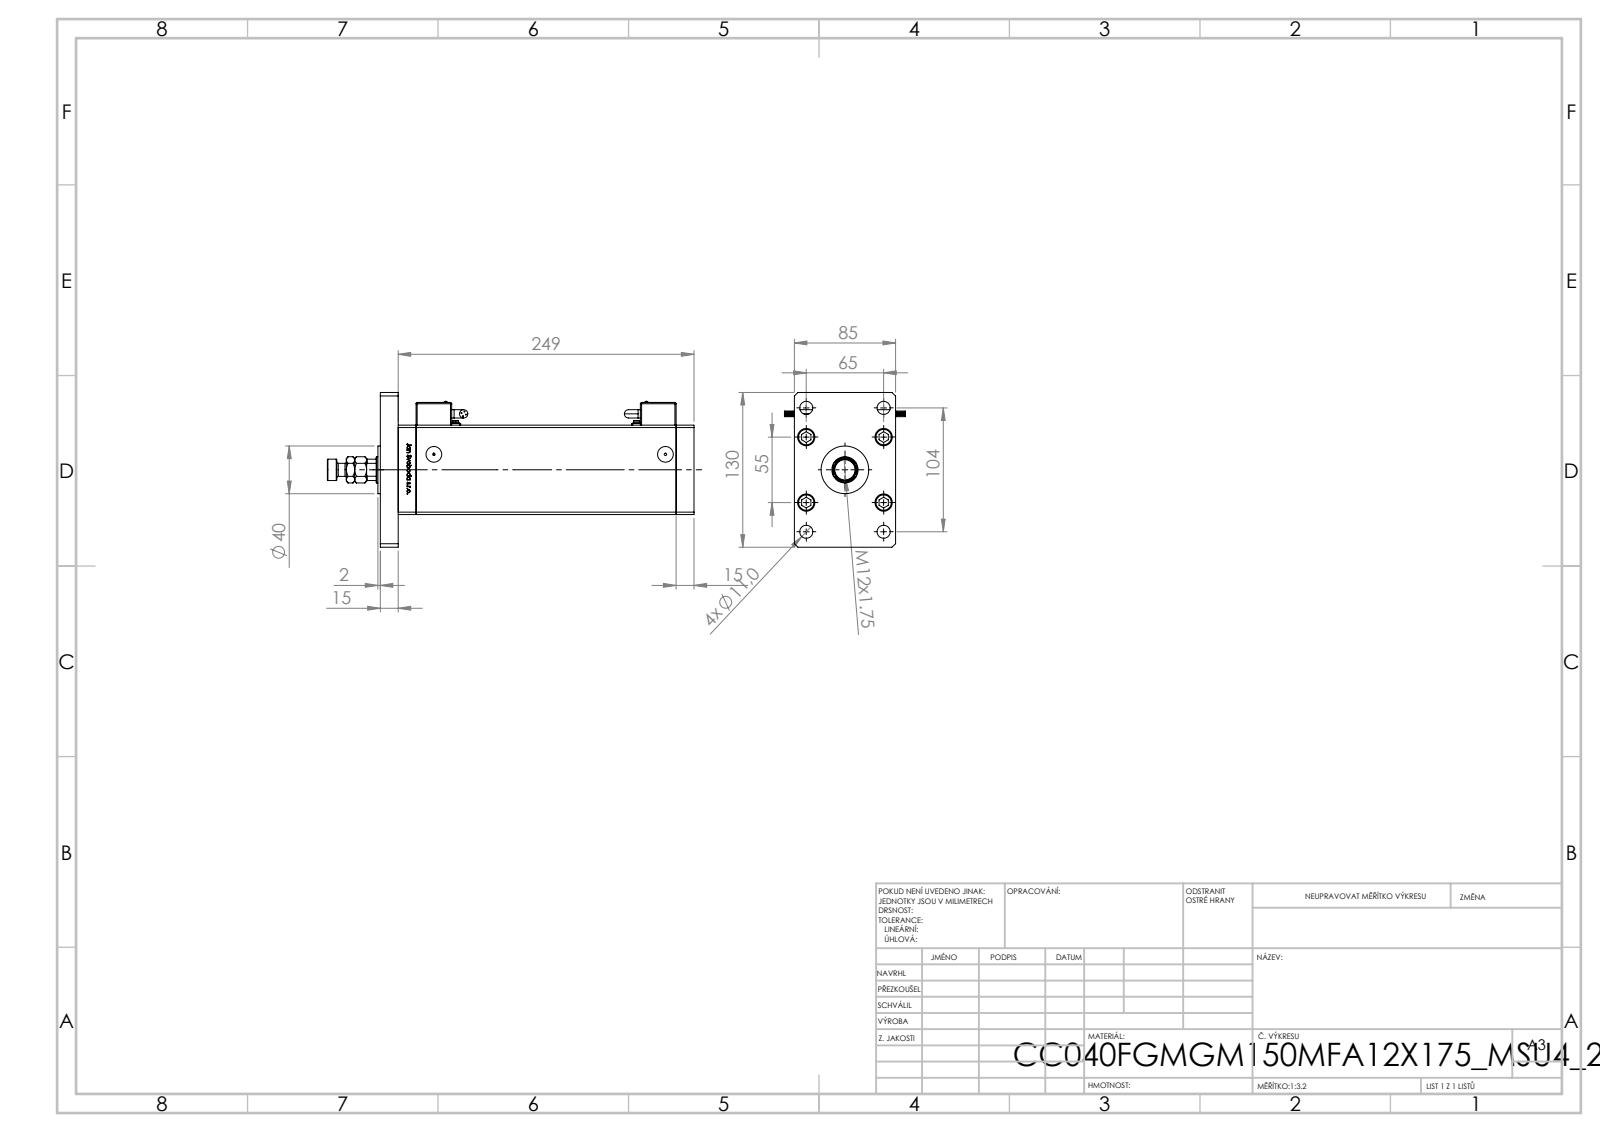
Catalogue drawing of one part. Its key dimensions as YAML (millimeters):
part_name: "V220C_F_MIDDLE; ALLEN BOLT; V220C_FRONT_F; V220C_F (+4 more)"
step_written_by: "SolidWorks 2019 (CONFIG_CONTROL_DESIGN)"
units: millimeters
bodies: {solids: 22, faces: 1564, planar: 609, cylindrical: 281, other: 674}
overall_size: [308, 130, 101.6]
volume: 1582000
surface_area: 250281
round_holes:
  - {diameter: 11, count: 9}
  - {diameter: 15.5, count: 5}
  - {diameter: 10, count: 4}
  - {diameter: 14.5, count: 4}
  - {diameter: 2, count: 2}
  - {diameter: 3.6, count: 2}
  - {diameter: 5, count: 2}
  - {diameter: 7, count: 2}
  - {diameter: 13.16, count: 2}
  - {diameter: 13.5, count: 1}
  - {diameter: 22, count: 1}
  - {diameter: 23.5, count: 1}
round_bosses_or_shafts:
  - {diameter: 8, count: 9}
  - {diameter: 0.85, count: 8}
  - {diameter: 14.5, count: 5}
  - {diameter: 7, count: 4}
  - {diameter: 6, count: 2}
  - {diameter: 3.5, count: 2}
  - {diameter: 2.5, count: 2}
  - {diameter: 40, count: 1}
partial_cylinders:
  - {radius: 1, count: 24}
  - {radius: 4, count: 4}
  - {radius: 0.93, count: 2}
  - {radius: 10.5, count: 1}
face_to_face_distances: [15, 85, 75, 233.5, 248.5, 30, 218.5, 263.5, 10.5, 68.5]
hole_center_spacings: [28, 24.5, 42.57, 61.32, 65, 69.46, 79.5, 102.69]
